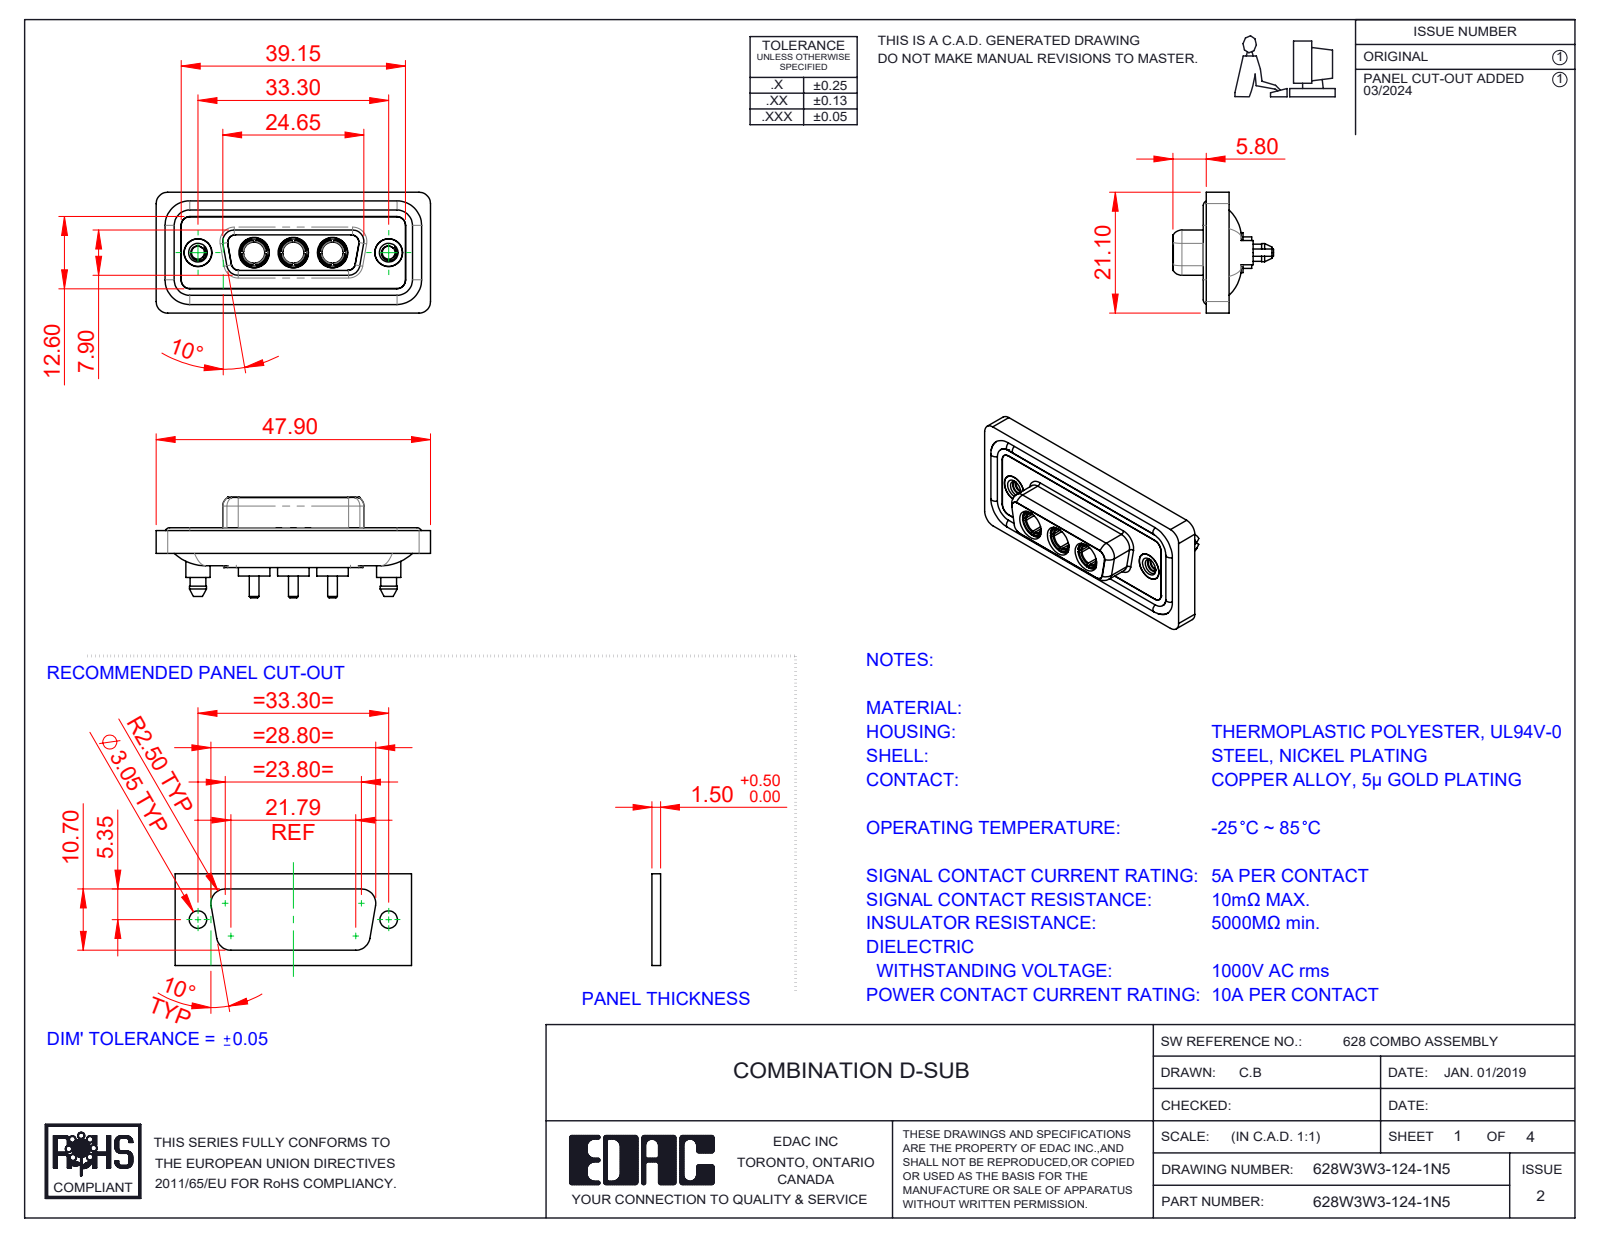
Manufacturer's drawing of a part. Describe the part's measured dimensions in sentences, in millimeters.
The part is named "628Combo Shell Rear_15 Contacts; 628Combo Waterproof Housing_15 Contacts; 628W3W3-124-1N5; Power Socket_10A S (+3 more)". Its 3-D file was written by "SolidWorks 2023 (CONFIG_CONTROL_DESIGN)". It is 13 solids with 658 faces: 208 planar, 289 cylindrical and 161 other. Overall it measures 47.9 by 21.1 by 17.55 millimeters. Its volume is 6 116 cubic millimeters and its surface area 10 034 square millimeters. Round holes: 5 of diameter 4.85, 3 of diameter 3.7, 3 of diameter 5.3, 2 of diameter 2.26, 2 of diameter 4, 2 of diameter 4.05, 2 of diameter 5. Round bosses or shafts: 4 of diameter 1.6, 3 of diameter 5.5, 3 of diameter 5.2, 3 of diameter 4.96, 3 of diameter 4.75, 3 of diameter 3.75, 3 of diameter 1.7, 2 of diameter 5.4. Partial cylindrical surfaces (rounded edges, fillets, slot ends): 24 of radius 1.5, 20 of radius 2, 12 of radius 1.35, 10 of radius 1.6, 4 of radius 0.25, 4 of radius 0.5, 4 of radius 0.6, 4 of radius 0.65. The main face-to-face distances are 0.4, 1.8, 1.6, 0.5, 7.45, 1.1, 2.9, 5.65, 7.05, 1.5. The hole center spacings are 6.85, 9.8, 16.65, 23.5, 13.7, 33.3.
